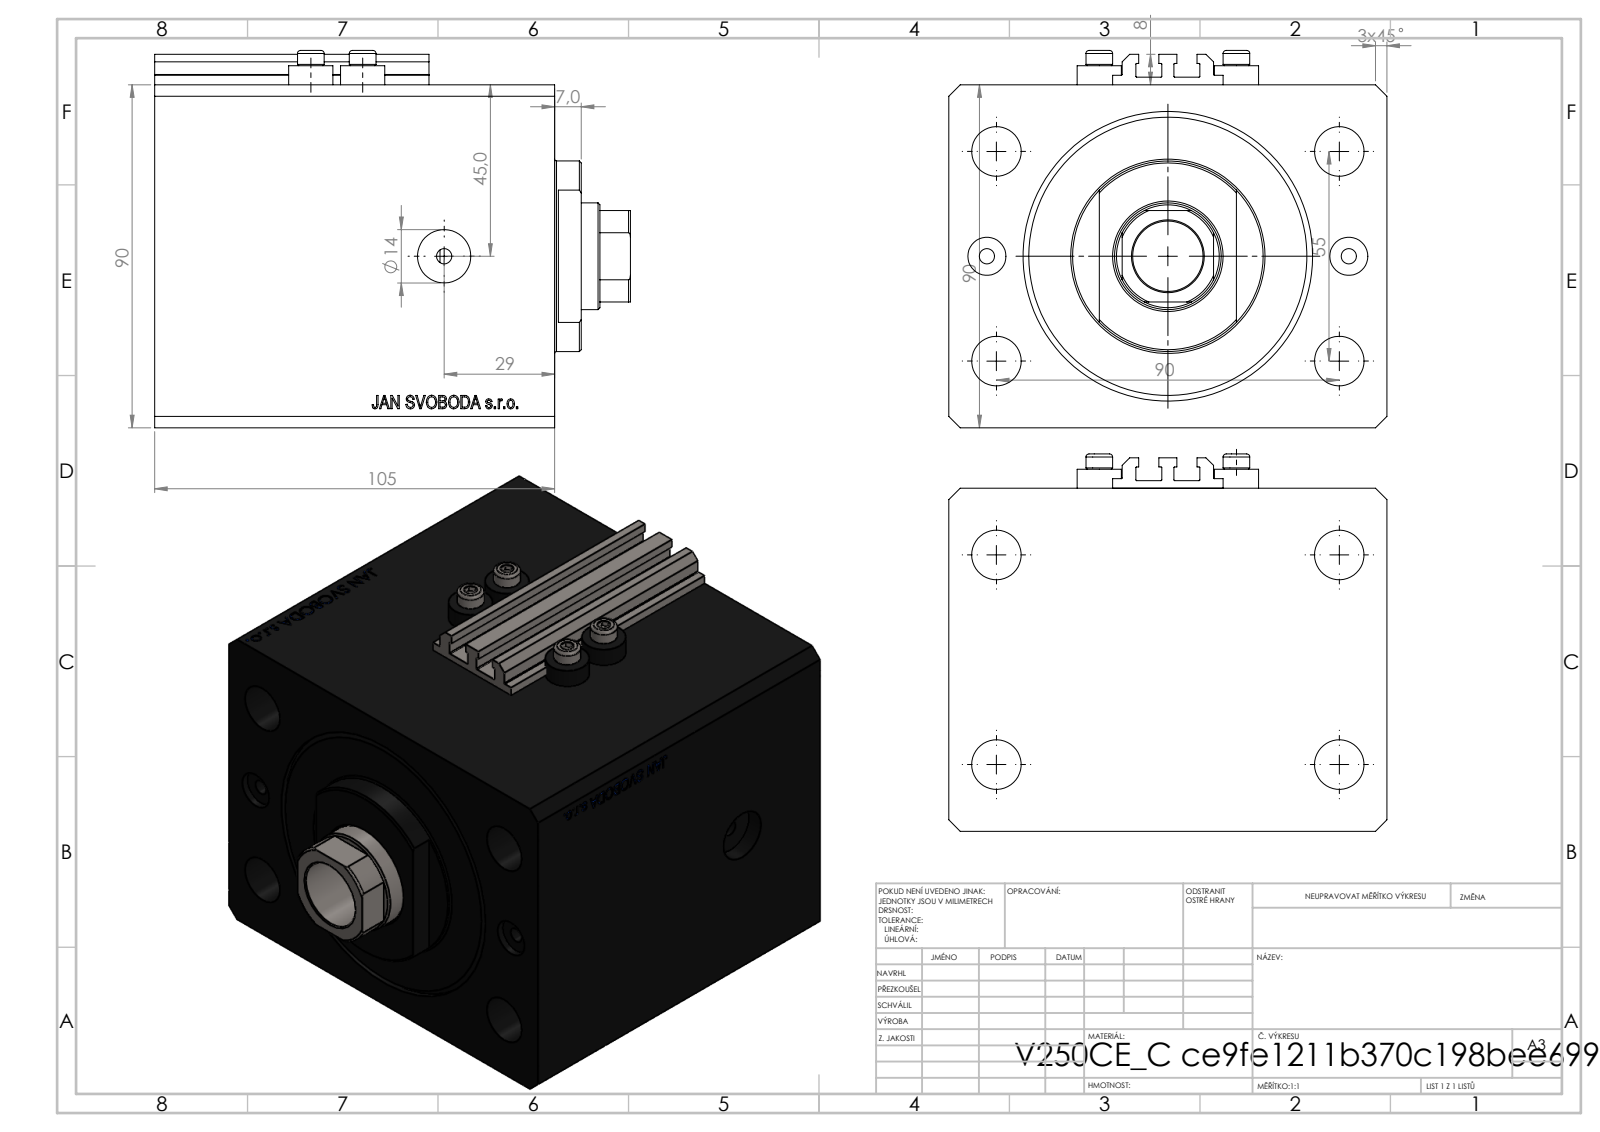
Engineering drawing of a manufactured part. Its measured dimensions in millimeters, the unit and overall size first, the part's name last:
Units: millimetres
Overall size (bounding box): 124.9 × 115 × 99
Round holes (diameter × count): ⌀4 ×8, ⌀13 ×4, ⌀10 ×2, ⌀14 ×2, ⌀18.5 ×1, ⌀28 ×1, ⌀63 ×1, ⌀76 ×1
Round bosses / shafts (diameter × count): ⌀11.6 ×4, ⌀7 ×4, ⌀50 ×1
Partial cylindrical surfaces — rounded edges, fillets, slot ends (radius × count): R0.2 ×10, R13.5 ×1
Main face-to-face distances: 90, 115, 105, 87.1, 17.9, 57, 74.9, 30.1, 54.9, 37
Hole centre spacings: 27.61, 52.74, 96.5, 13.6, 36, 38.48, 47.5, 55
Volume: 996 680 mm³ · Surface area: 150 304 mm²
Bodies: 8 solids, 1034 faces (504 planar, 86 cylindrical, 444 other)
Part name (STEP PRODUCT): V250CE_VC_C; V250CE_C_Body; ALLEN BOLT V250CE; V250CE_C_VCP
STEP written by: SolidWorks 2019 (CONFIG_CONTROL_DESIGN)
